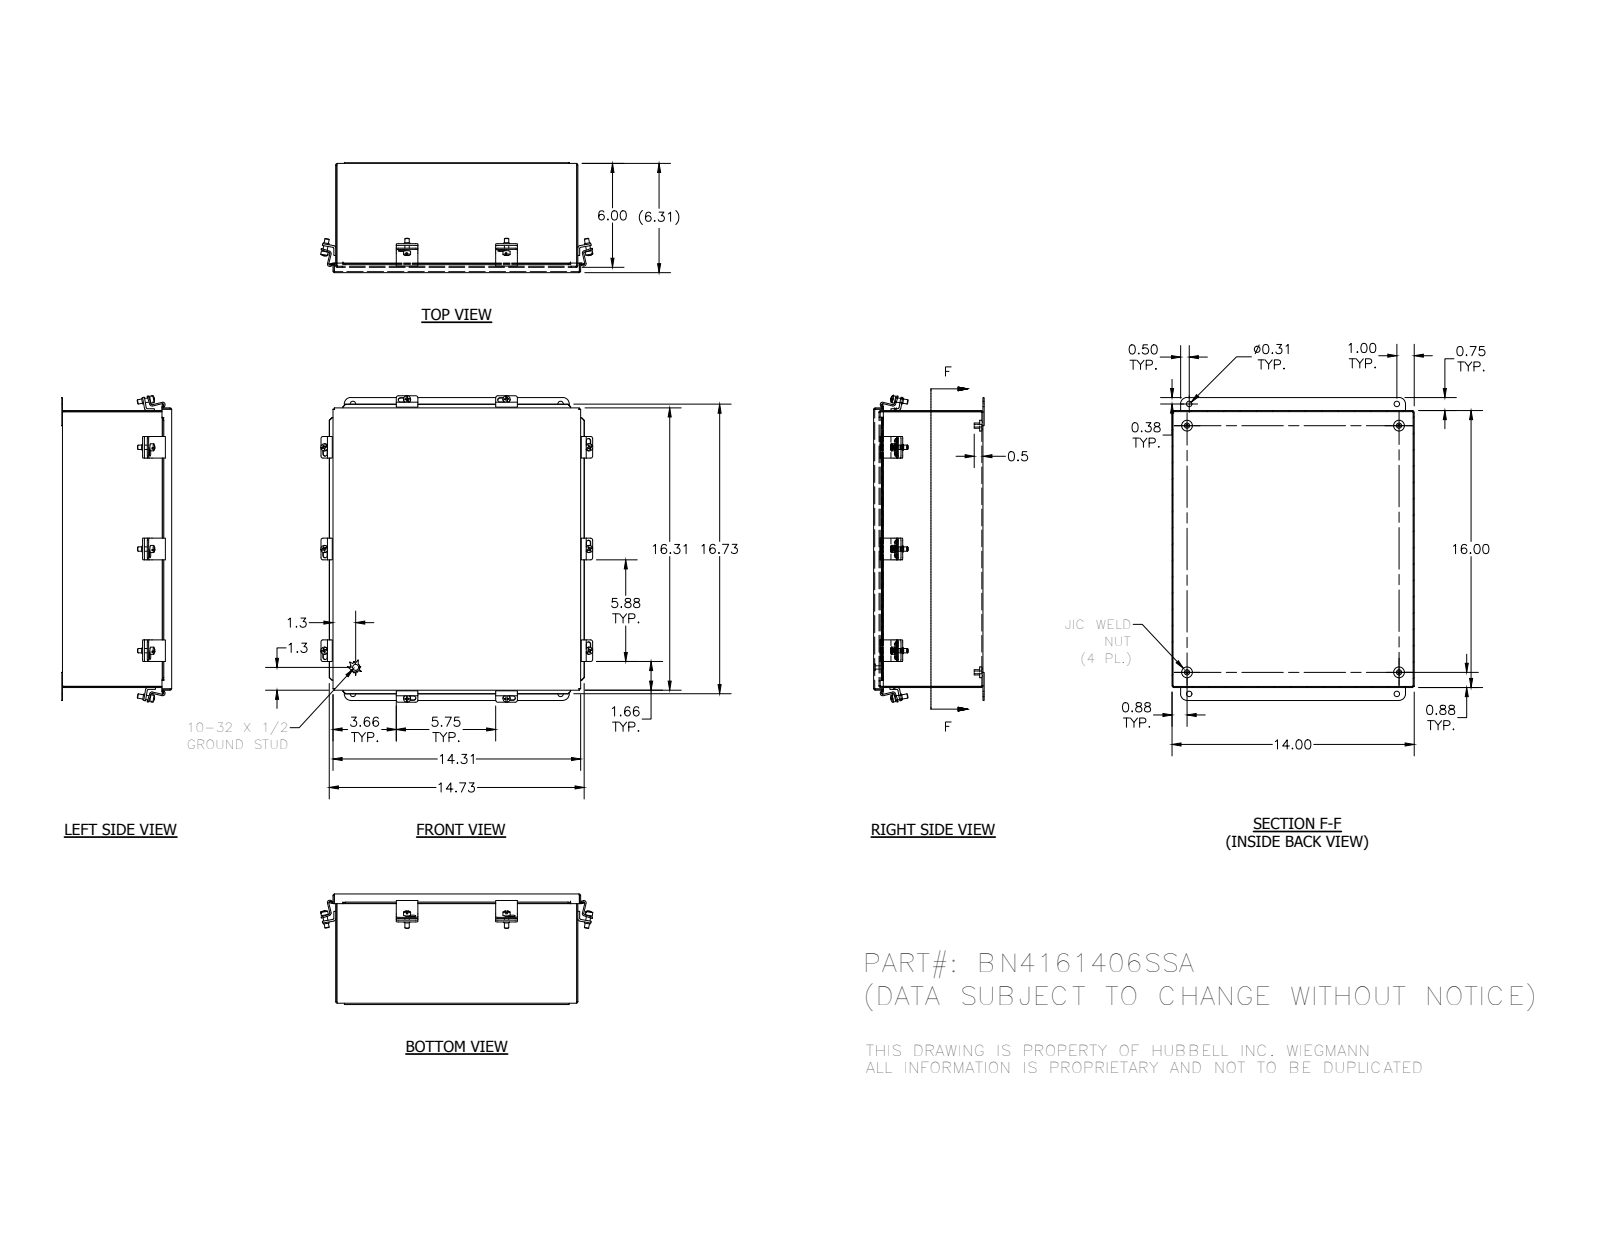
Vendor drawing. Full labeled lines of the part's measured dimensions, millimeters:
Part name (STEP PRODUCT): 30811_1; BN4161406SSABKP_1; BN4161406SSA; 372164_1 (+5 more)
STEP written by: SolidWorks 2014 (AUTOMOTIVE_DESIGN)
Units: millimetres
Bodies: 39 solids, 1081 faces (515 planar, 392 cylindrical, 174 other)
Overall size (bounding box): 449.9 × 399.4 × 162.3
Volume: 998 600 mm³ · Surface area: 1 241 000 mm²
Round holes (diameter × count): ⌀2.8 ×16, ⌀5 ×10, ⌀4 ×4, ⌀7.9 ×4
Round bosses / shafts (diameter × count): ⌀10.4 ×10, ⌀8.7 ×10, ⌀6.4 ×10, ⌀15.9 ×4, ⌀7.6 ×4, ⌀8.6 ×1, ⌀4.8 ×1
Partial cylindrical surfaces — rounded edges, fillets, slot ends (radius × count): R3.2 ×40, R3.4 ×20, R0.8 ×16, R2.4 ×16, R1.6 ×12, R3.2 ×12, R9.5 ×4
Main face-to-face distances: 1.6, 158.8, 160.4, 157.1, 354, 404.8, 355.6, 352.4, 406.4, 403.2
Hole centre spacings: 19.1, 146.1, 149.2, 149.2, 1.6, 19.1, 31.9, 146.1
